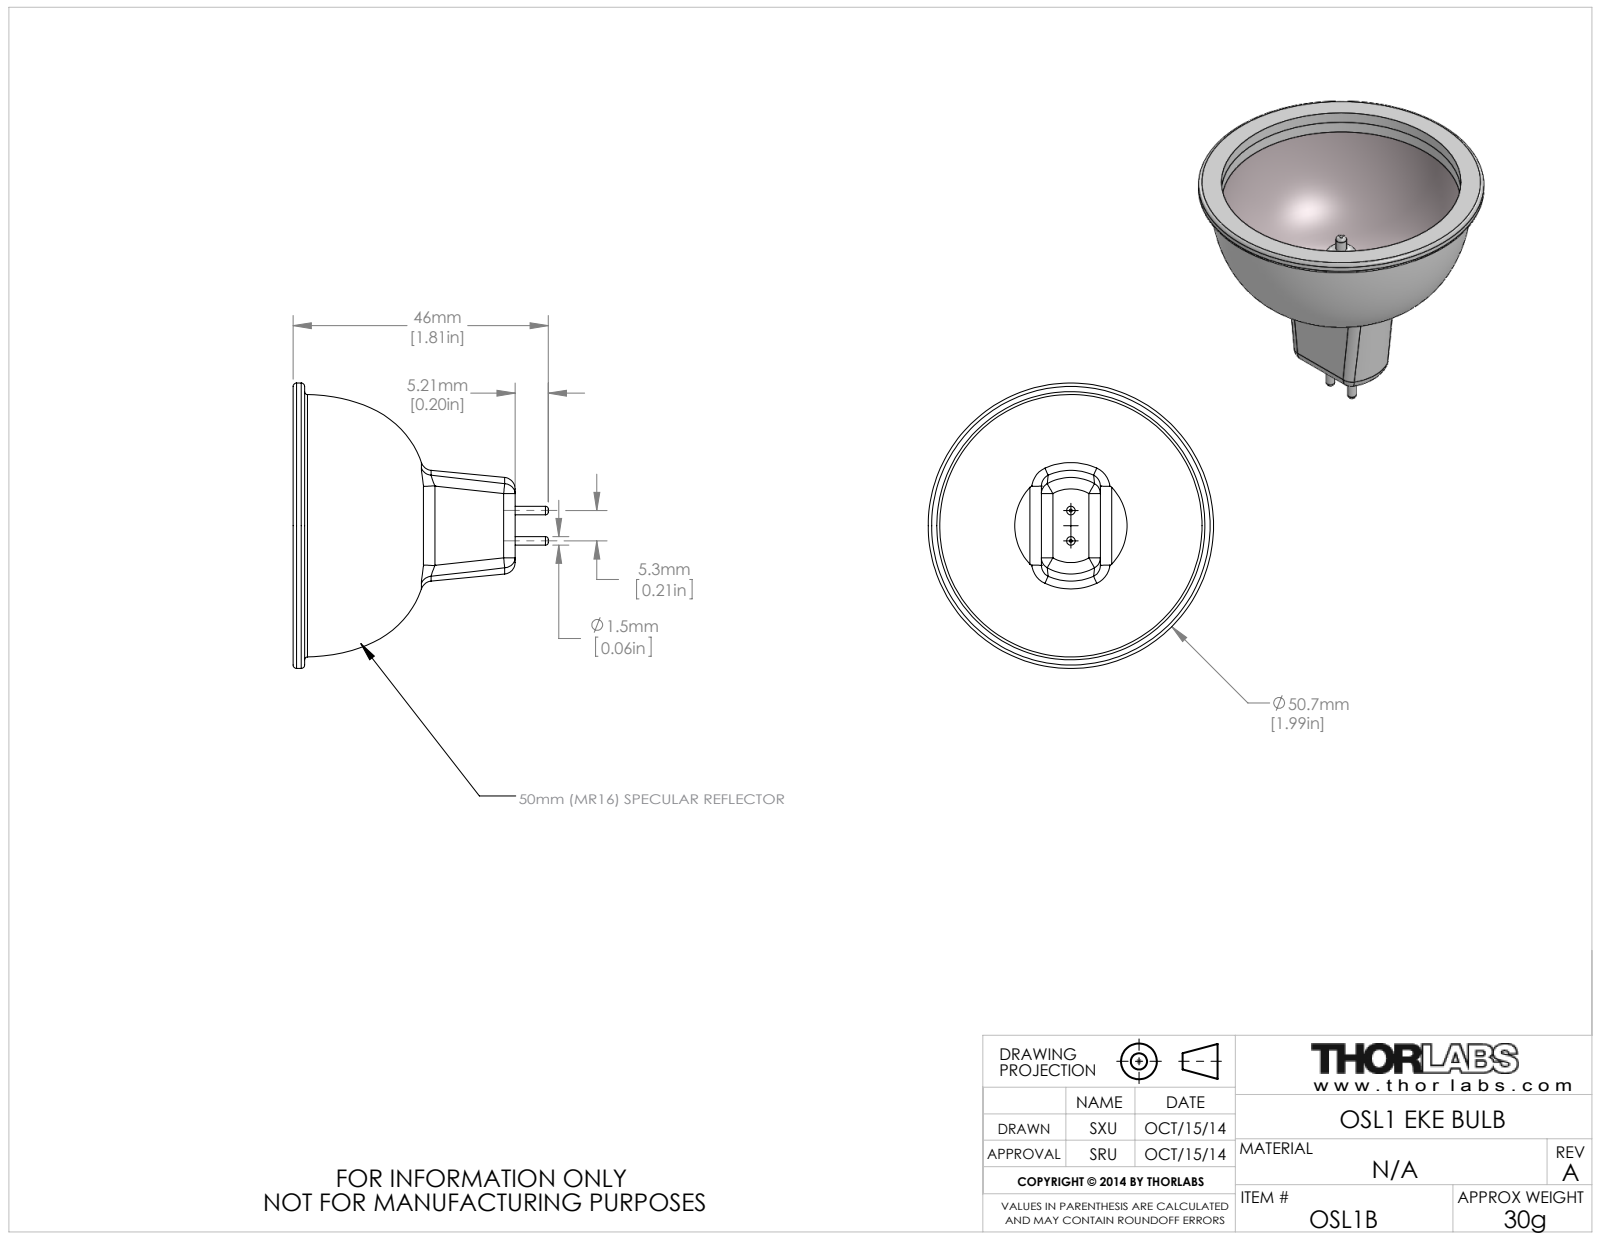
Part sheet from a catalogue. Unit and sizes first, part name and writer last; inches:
Units: inches
Overall size (bounding box): 1.961 × 1.961 × 1.754
Round holes (diameter × count): ⌀1.646 ×1
Round bosses / shafts (diameter × count): ⌀0.059 ×2, ⌀1.961 ×1, ⌀0.231 ×1, ⌀0.073 ×1
Partial cylindrical surfaces — rounded edges, fillets, slot ends (radius × count): R0.079 ×4
Main face-to-face distances: 0.832, 0.406, 0.754, 0.079, 0.693, 1.447, 1.526, 0.63, 0.063, 0.817
Volume: 0.628 in³ · Surface area: 13.17 in²
Bodies: 1 solid, 65 faces (11 planar, 16 cylindrical, 38 other)
Part name (STEP PRODUCT): TTN018294-E0W
STEP written by: SolidWorks 2014 (CONFIG_CONTROL_DESIGN)
